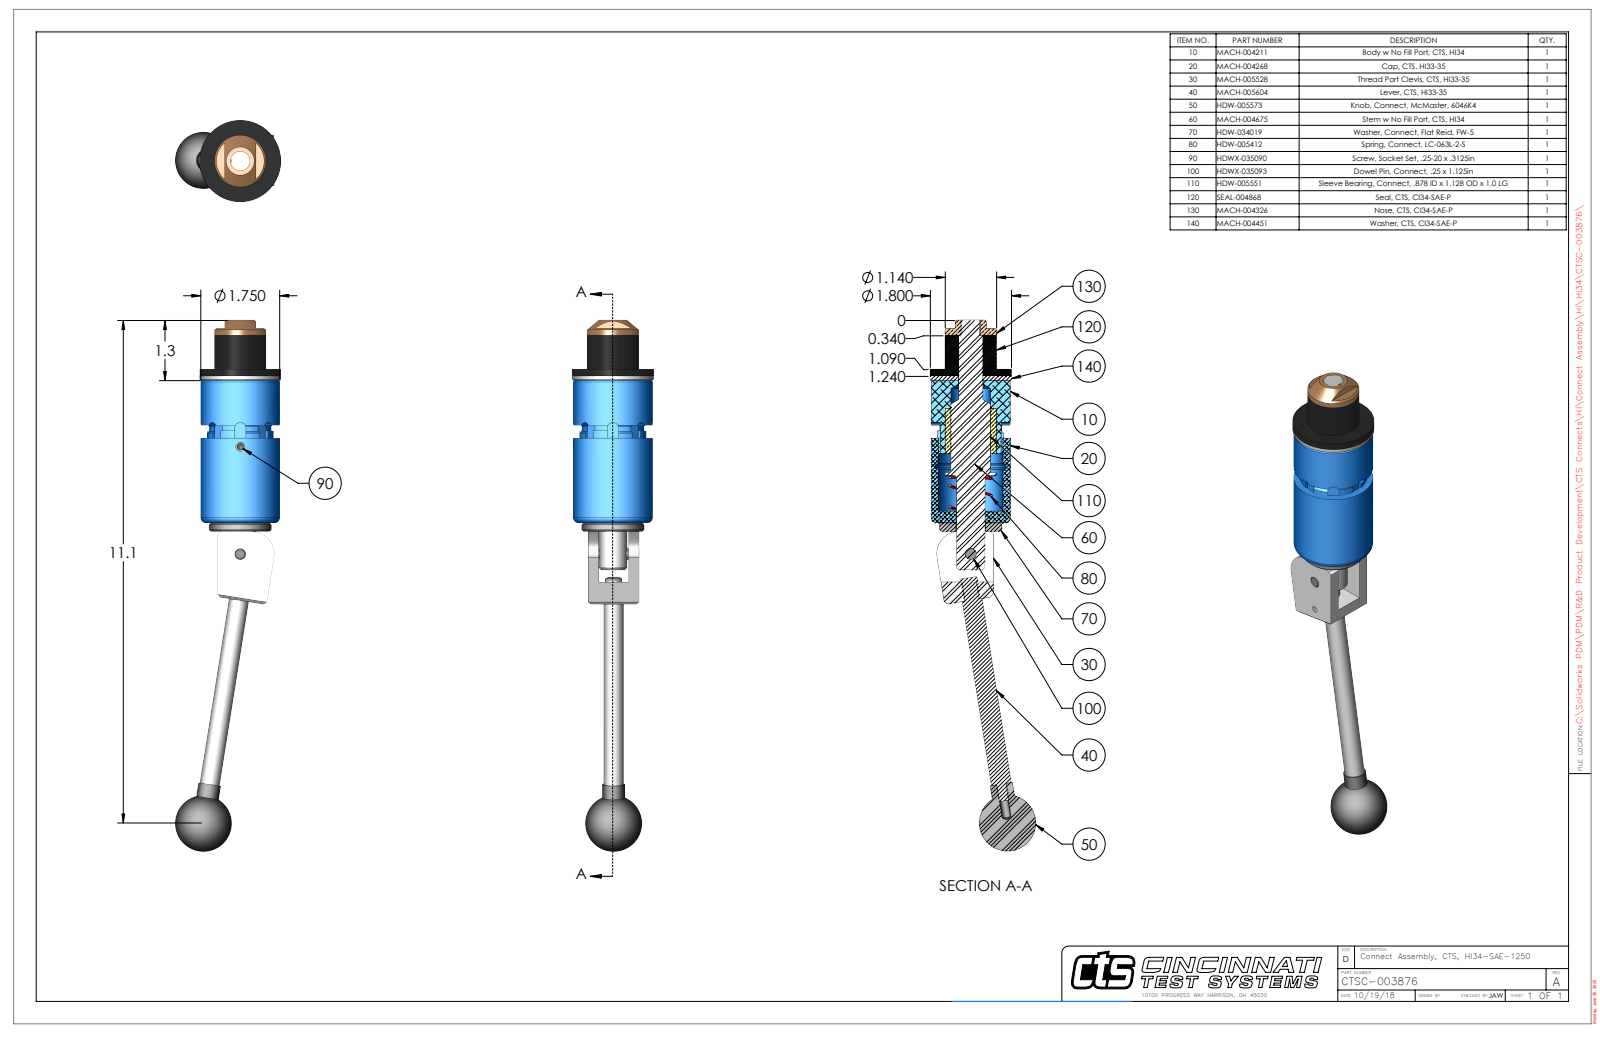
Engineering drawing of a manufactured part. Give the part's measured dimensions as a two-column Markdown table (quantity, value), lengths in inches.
| quantity | value |
| --- | --- |
| part name | CTSC-003876 |
| STEP written by | SolidWorks 2023 (AUTOMOTIVE_DESIGN) |
| units | inches |
| bodies | 9 solids, 280 faces (107 planar, 114 cylindrical, 59 other) |
| overall size | 11.77 × 2.337 × 1.8 |
| volume | 12.33 in³ |
| surface area | 74.86 in² |
| round holes (diameter × count) | 0.201 × 2, 0.15 × 1, 0.249 × 1, 0.251 × 1, 0.313 × 1, 0.422 × 1, 0.53 × 1, 0.541 × 1, 0.547 × 1, 0.635 × 1, 0.656 × 1 |
| round bosses / shafts (diameter × count) | 0.5 × 2, 0.44 × 2, 0.25 × 2, 1.8 × 1, 1.75 × 1, 1.38 × 1, 1.14 × 1, 0.625 × 1 |
| partial cylindrical surfaces (radius × count) | 0.125 × 4, 0.029 × 2, 0.5 × 1, 0.695 × 1, 0.709 × 1, 0.744 × 1, 0.797 × 1 |
| main face-to-face distances | 0.094, 3.255, 3.161, 1.12, 0.9, 0.994, 4.155, 0.75, 0.15, 0.244 |
| hole center spacings | 0.74, 2.376, 3.116 |
